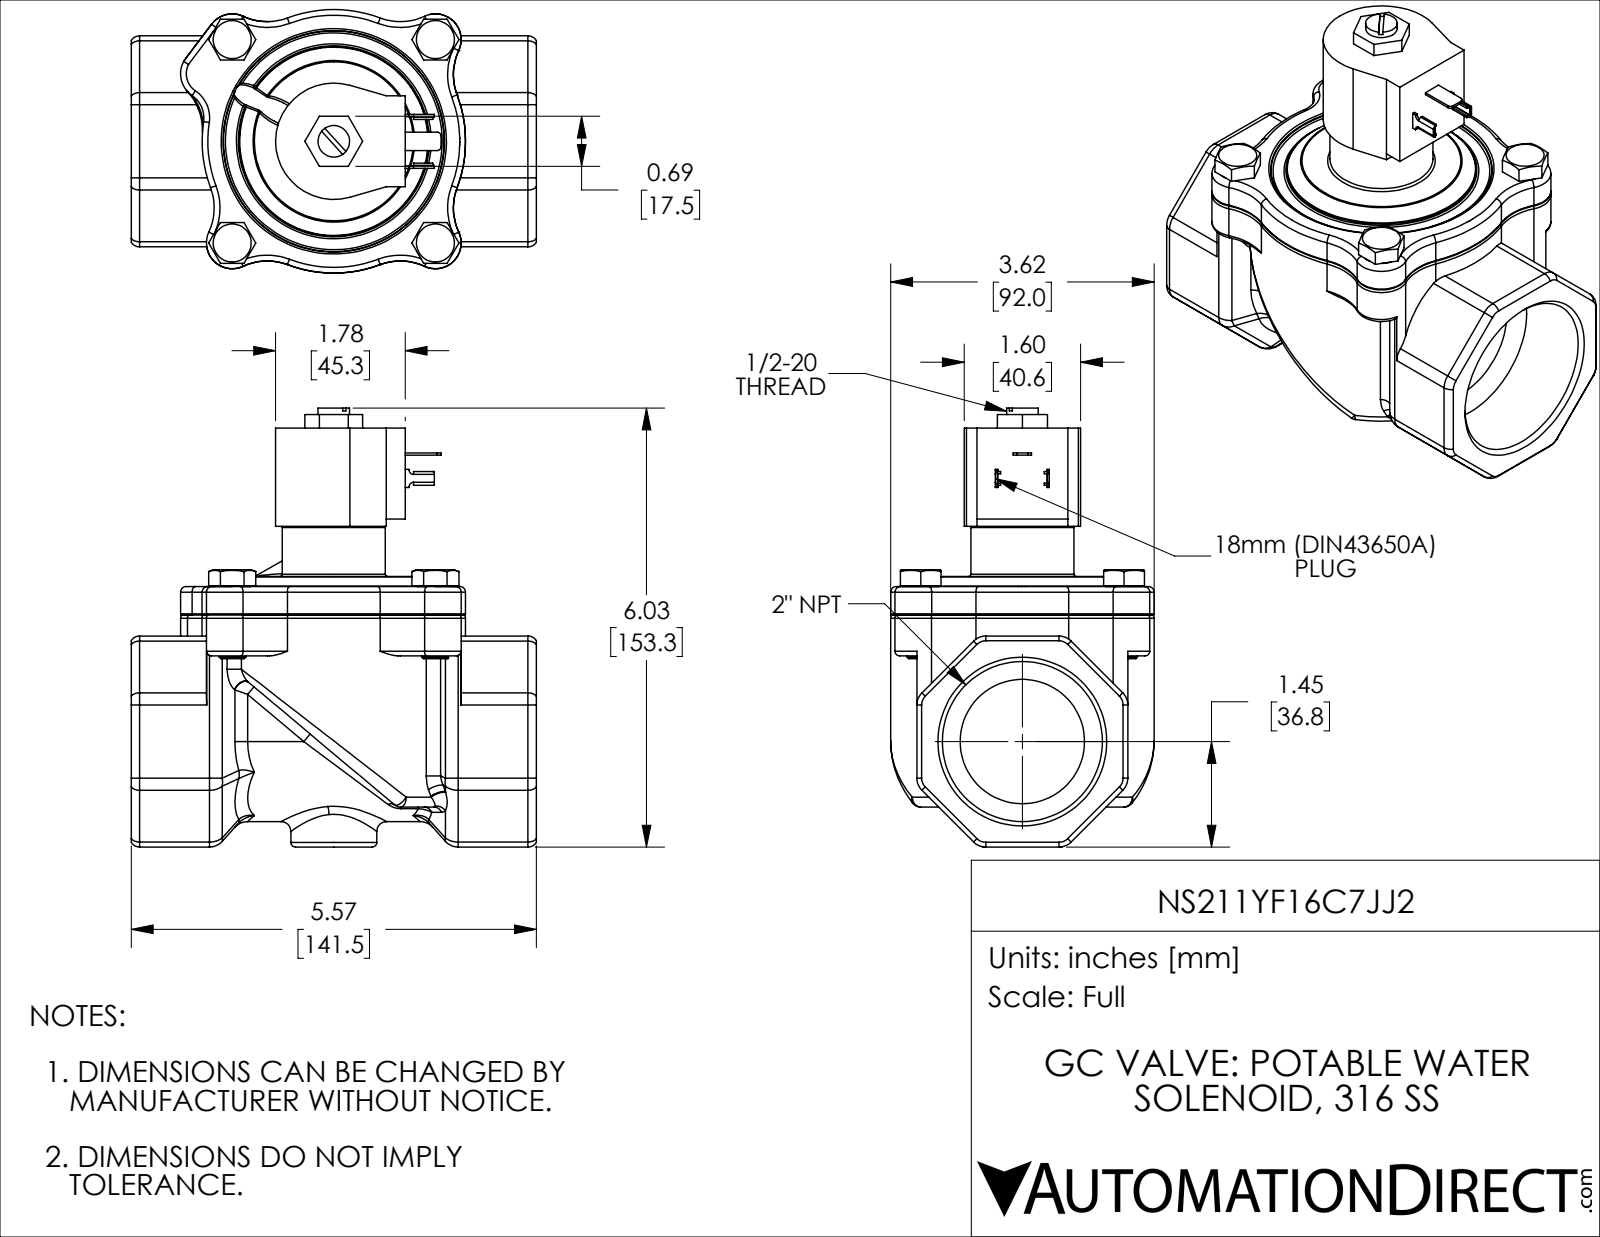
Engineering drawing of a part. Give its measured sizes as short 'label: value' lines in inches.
name: NS211YF16C7JJ2
written by: SolidWorks 2018 (AUTOMOTIVE_DESIGN)
unit: in
bodies: 9 solids, 606 faces (166 planar, 205 cylindrical, 235 other)
size: 6.034 × 5.571 × 3.622
volume: 37.3 in³; area: 171.8 in²
holes: 4× ⌀0.31, 4× ⌀0.433, 1× ⌀0.12, 1× ⌀0.125, 1× ⌀0.236, 1× ⌀0.434, 1× ⌀0.504, 1× ⌀0.846, 1× ⌀0.949, 1× ⌀1.71, 1× ⌀2.2, 1× ⌀2.874
bosses: 4× ⌀0.504, 4× ⌀0.37, 1× ⌀3.024, 1× ⌀1.417, 1× ⌀1.181
rounds: 29× R0.136, 28× R0.236, 15× R0.787, 8× R0.354, 4× R0.006, 4× R0.041, 2× R0.05, 2× R0.06
face distances: 0.118, 2.207, 3.364, 2.9, 2.9, 0.511, 0.393, 1.35, 1.338, 1.22
hole spacings: 1.976, 1.976, 2.795, 2.795, 1.976, 2.351, 2.794, 2.796
